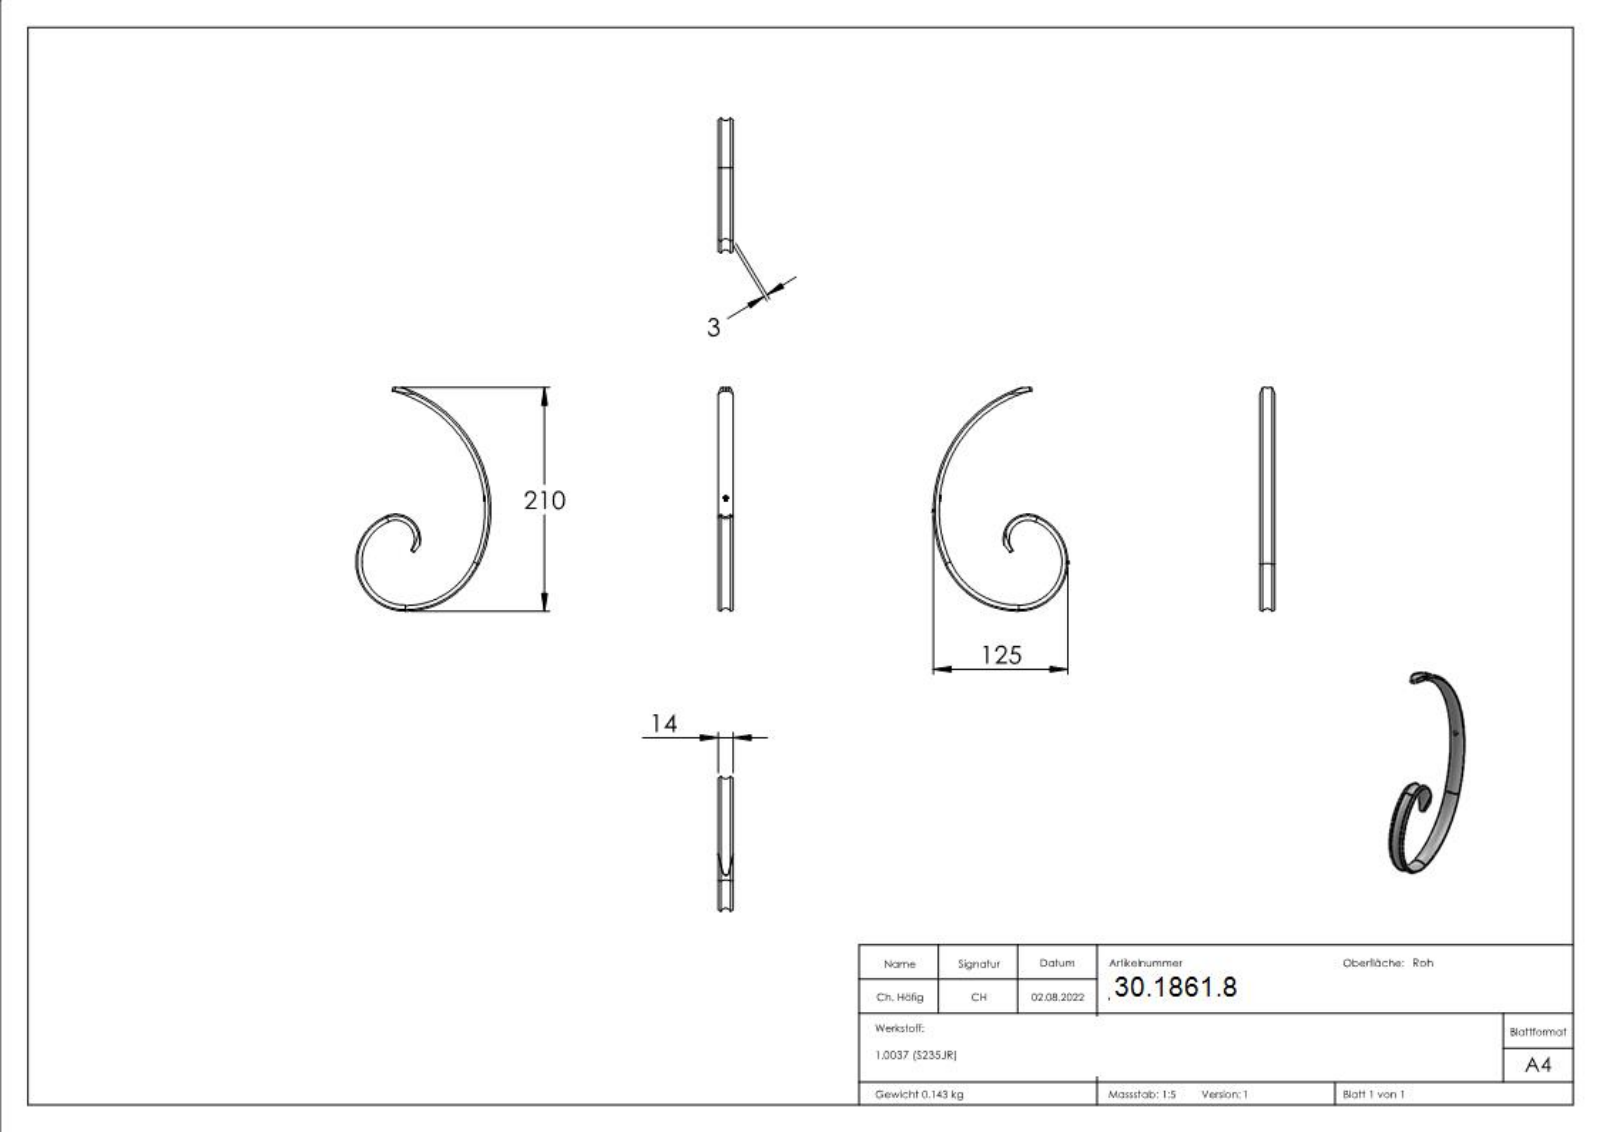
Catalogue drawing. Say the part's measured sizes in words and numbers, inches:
The part is named "5521". Its 3-D file was written by "SolidWorks 2018 (CONFIG_CONTROL_DESIGN)". It is 1 solid with 232 faces: 106 planar, 4 cylindrical and 122 other. Overall it measures 8.189 by 4.921 by 0.551 inches. Its volume is 1.119 cubic inches and its surface area 23.4 square inches. Partial cylindrical surfaces (rounded edges, fillets, slot ends): 2 of radius 0.059, 2 of radius 0.098. The main face-to-face distances are 0.029, 0.091, 0.062, 0.088, 0.048, 0.031, 0.103, 0.077, 0.014, 0.044.
